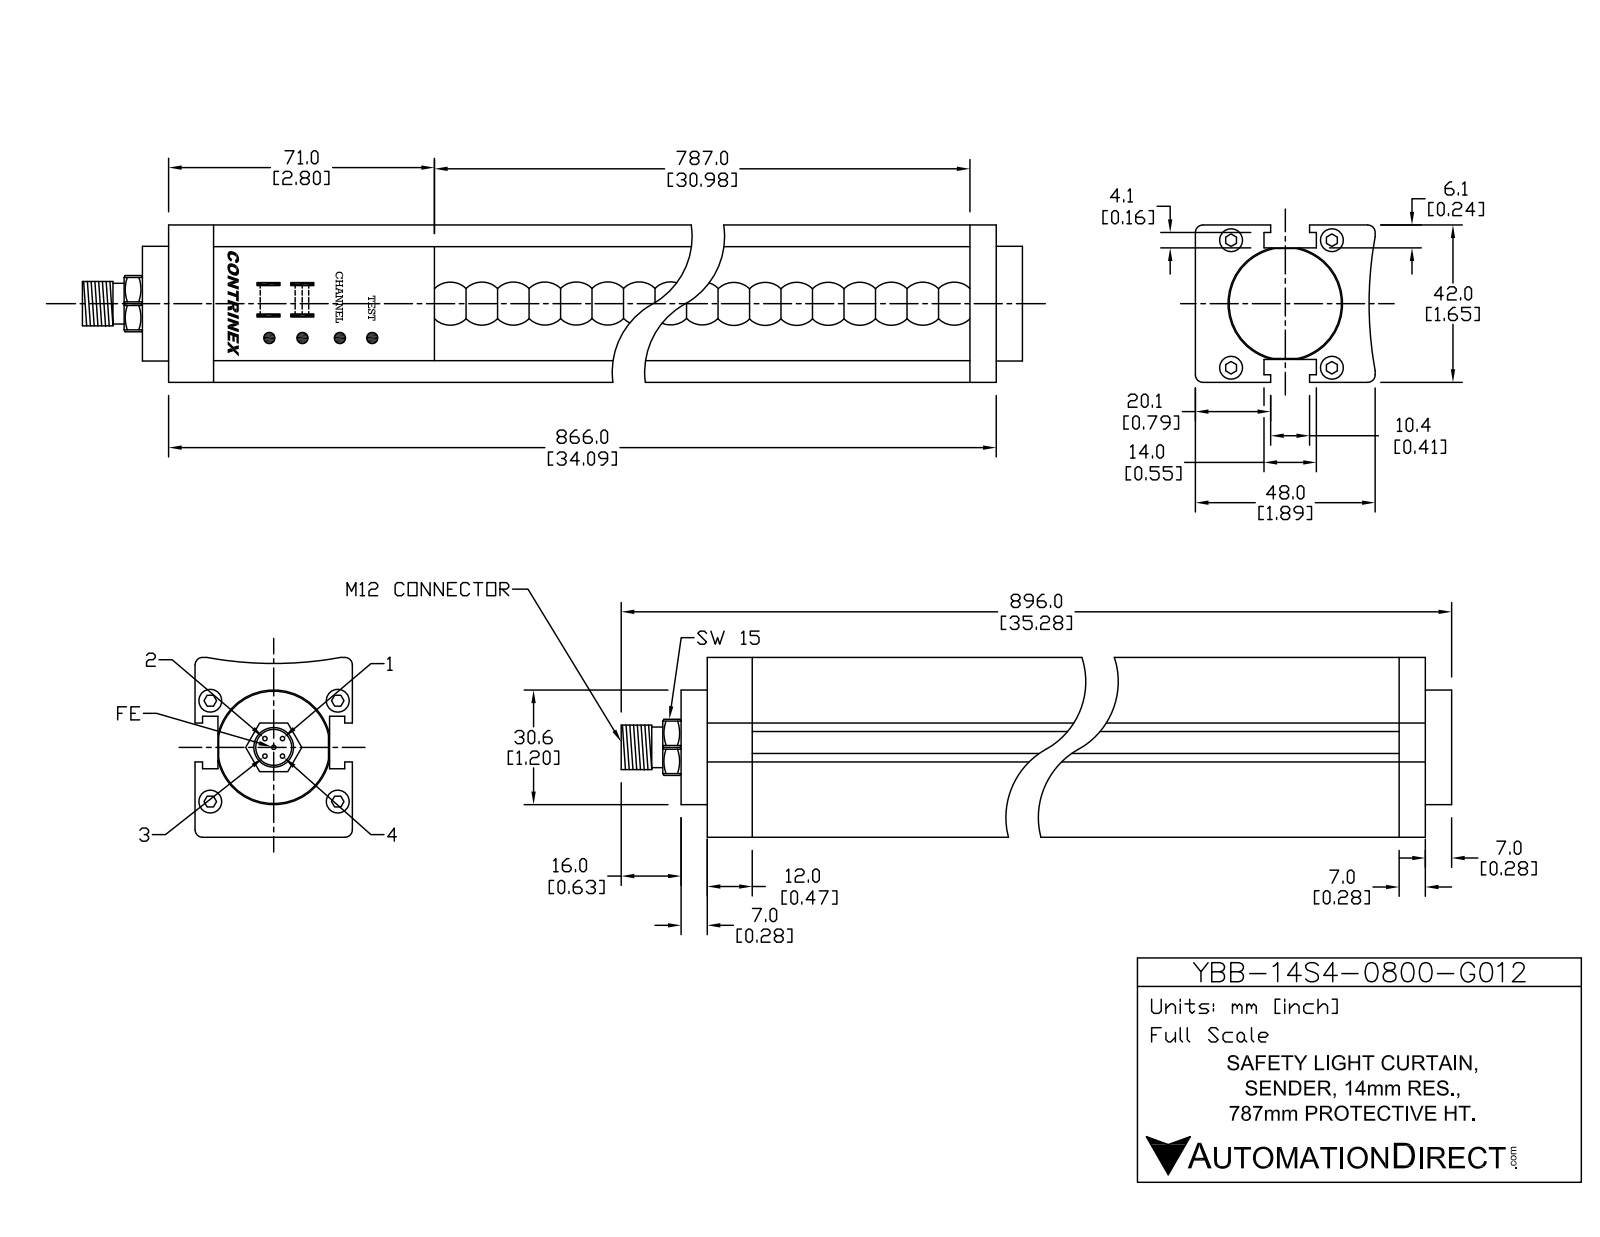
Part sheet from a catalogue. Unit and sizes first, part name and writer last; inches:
Units: inches
Overall size (bounding box): 35.276 × 1.89 × 1.654
Round holes (diameter × count): ⌀0.236 ×4, ⌀0.335 ×1, ⌀1.26 ×1
Round bosses / shafts (diameter × count): ⌀0.039 ×5, ⌀0.217 ×4, ⌀1.205 ×1, ⌀0.472 ×1, ⌀0.413 ×1
Partial cylindrical surfaces — rounded edges, fillets, slot ends (radius × count): R0.039 ×48, R0.02 ×4, R0.022 ×2, R0.323 ×1, R3.937 ×1
Main face-to-face distances: 0.248, 1.406, 1.654, 1.157, 0.551, 0.677, 1.228, 0.618, 1.169, 1.846
Hole centre spacings: 0.828, 0.88, 1.059, 1.339, 1.707
Volume: 95.26 in³ · Surface area: 313.7 in²
Bodies: 19 solids, 440 faces (208 planar, 168 cylindrical, 64 other)
Part name (STEP PRODUCT): YBB-14S4-0800-G012
STEP written by: SolidWorks 2016 (AUTOMOTIVE_DESIGN)
